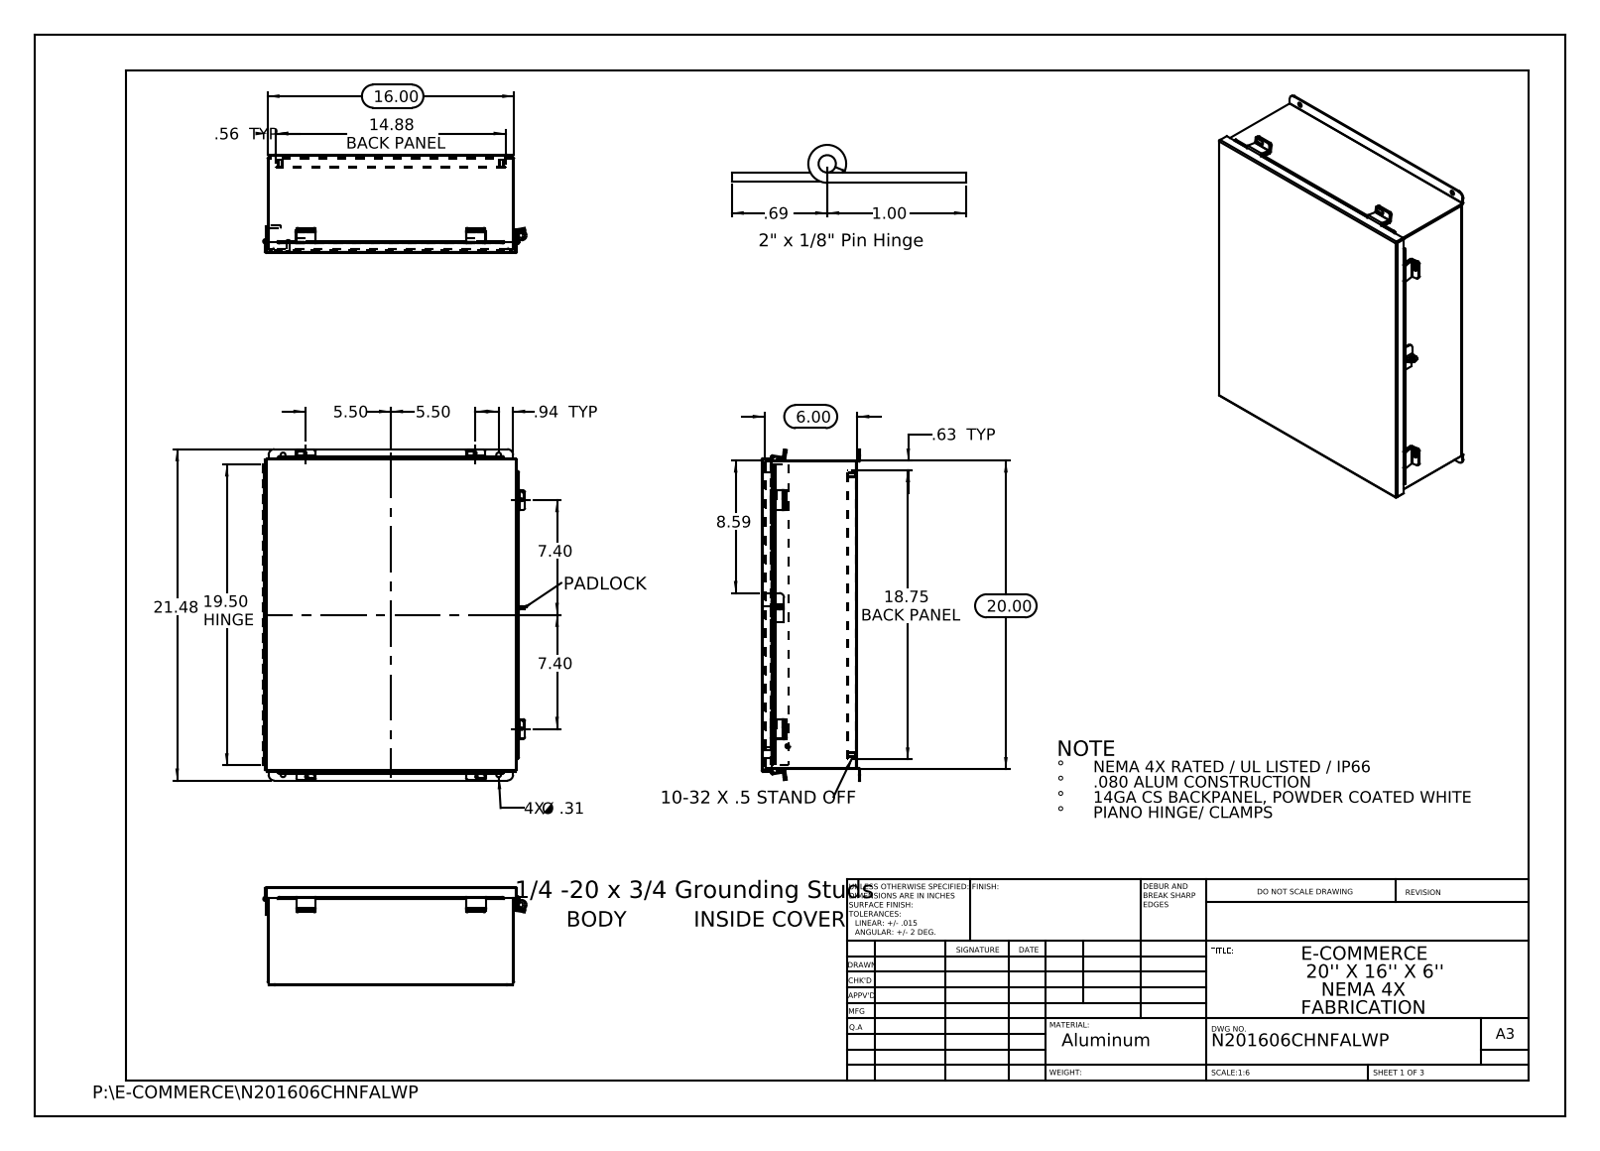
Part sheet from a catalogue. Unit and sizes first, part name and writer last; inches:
Units: inches
Overall size (bounding box): 21.476 × 17.072 × 6.39
Round holes (diameter × count): ⌀0.25 ×10, ⌀0.187 ×4, ⌀0.312 ×4, ⌀0.125 ×1, ⌀0.125 ×1, ⌀0.373 ×1, ⌀0.375 ×1
Round bosses / shafts (diameter × count): ⌀0.313 ×4, ⌀0.315 ×2, ⌀0.236 ×2, ⌀0.273 ×1, ⌀0.25 ×1
Partial cylindrical surfaces — rounded edges, fillets, slot ends (radius × count): R0.125 ×21, R0.013 ×13, R0.009 ×12, R0.088 ×12, R0.133 ×12, R0.083 ×6, R0.1 ×6, R0.375 ×4
Main face-to-face distances: 0.075, 6.128, 6.053, 6.203, 0.074, 5.628, 0.575, 0.5, 5.553, 0.649
Hole centre spacings: 1.315, 14.235, 19.427, 24.048, 11, 13.976, 14.375, 18.126
Volume: 113 in³ · Surface area: 3 067 in²
Bodies: 27 solids, 938 faces (579 planar, 339 cylindrical, 20 other)
Part name (STEP PRODUCT): N201606CHNFALWP JIC_Standoff; N201606CHNFALWP JIC Clamp Bracket; HW-CLH-JH-20154; N201606CHNFALWP JIC Bottom (+8 more)
STEP written by: SolidWorks 2013 (CONFIG_CONTROL_DESIGN)
